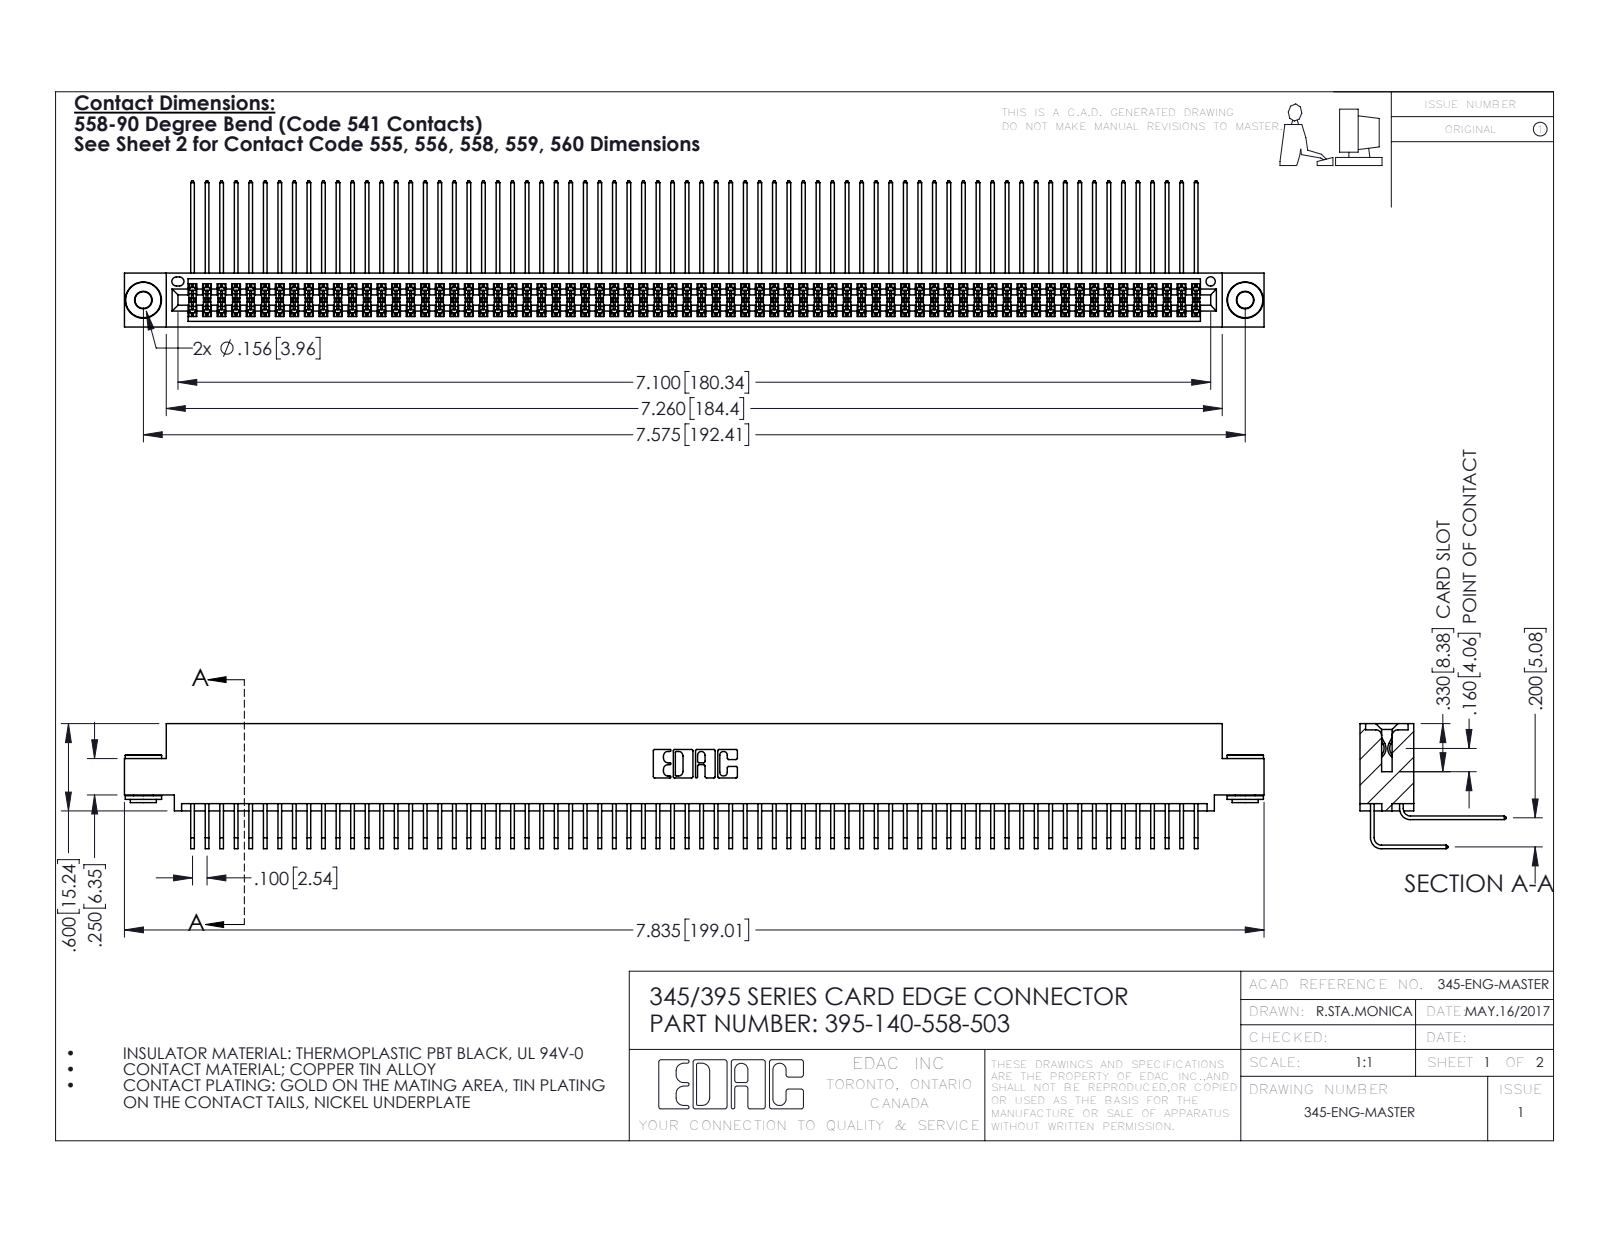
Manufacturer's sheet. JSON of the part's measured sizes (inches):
{"part_name": "345-292-001_558 559 Tail - 1; 345 Part_0.110 Offset - 0.156 Dia-TH; 345-292-001_558 Tail - 2; 345-250-002_345-250-002-102 (+1 more)", "step_written_by": "SolidWorks 2016 (CONFIG_CONTROL_DESIGN)", "units": "inches", "bodies": {"solids": 143, "faces": 7448, "planar": 4994, "cylindrical": 2446, "other": 8}, "overall_size": [7.835, 1.005, 0.859], "volume_in3": 1.242, "surface_area_in2": 53.8, "round_holes": [[0.116, 2], [0.156, 2], [0.064, 1]], "round_bosses_or_shafts": [[0.25, 2], [0.18, 2], [0.136, 2]], "partial_cylinders_radius": [[0.006, 279], [0.01, 22], [0.007, 6], [0.031, 6], [0.026, 3], [0.014, 2], [0.019, 2], [0.022, 2]], "face_to_face_distances": [0.072, 0.298, 0.2, 0.025, 0.37, 0.098, 0.272, 0.225, 0.025, 0.175], "hole_center_spacings": [0.27, 7.339, 7.575]}
